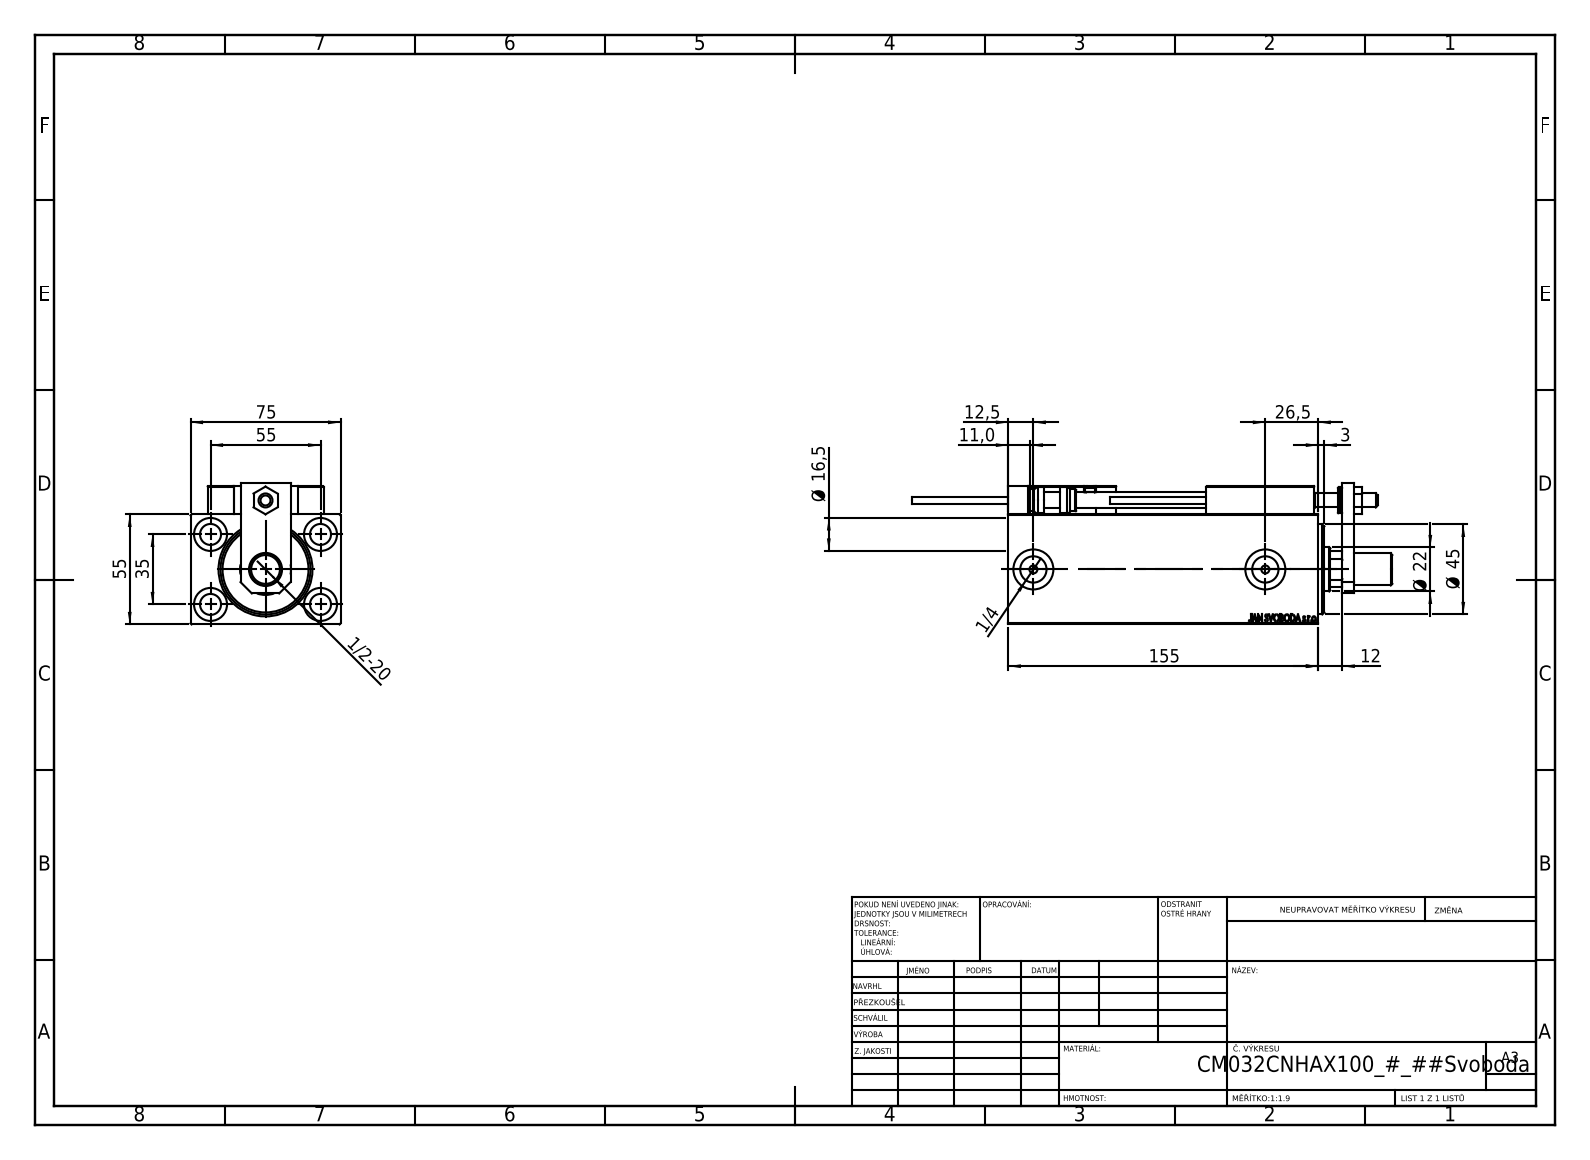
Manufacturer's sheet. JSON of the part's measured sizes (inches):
{"part_name": "ALLEN BOLT D5; MAGNET; TYC_L79; SWITCH X (+7 more)", "step_written_by": "SolidWorks 2019 (CONFIG_CONTROL_DESIGN)", "units": "inches", "bodies": {"solids": 24, "faces": 1295, "planar": 563, "cylindrical": 192, "other": 540}, "overall_size": [9.449, 2.953, 2.776], "volume_in3": 36.03, "surface_area_in2": 206.1, "round_holes": [[0.157, 6], [0.315, 5], [0.413, 5], [0.65, 5], [0.126, 4], [0.197, 2], [0.518, 2], [0.787, 2], [0.276, 1], [0.866, 1], [1.004, 1], [1.26, 1]], "round_bosses_or_shafts": [[0.197, 2], [0.15, 2], [0.63, 1], [0.551, 1], [0.512, 1], [0.433, 1]], "partial_cylinders_radius": [[0.012, 30], [0.118, 2], [0.413, 1]], "face_to_face_distances": [2.165, 2.953, 0.551, 0.472, 0.394, 0.276, 2.717, 0.984, 0.591, 0.197], "hole_center_spacings": [1.283, 0.448, 0.787, 1.165, 1.169, 1.273, 1.378, 1.42]}
